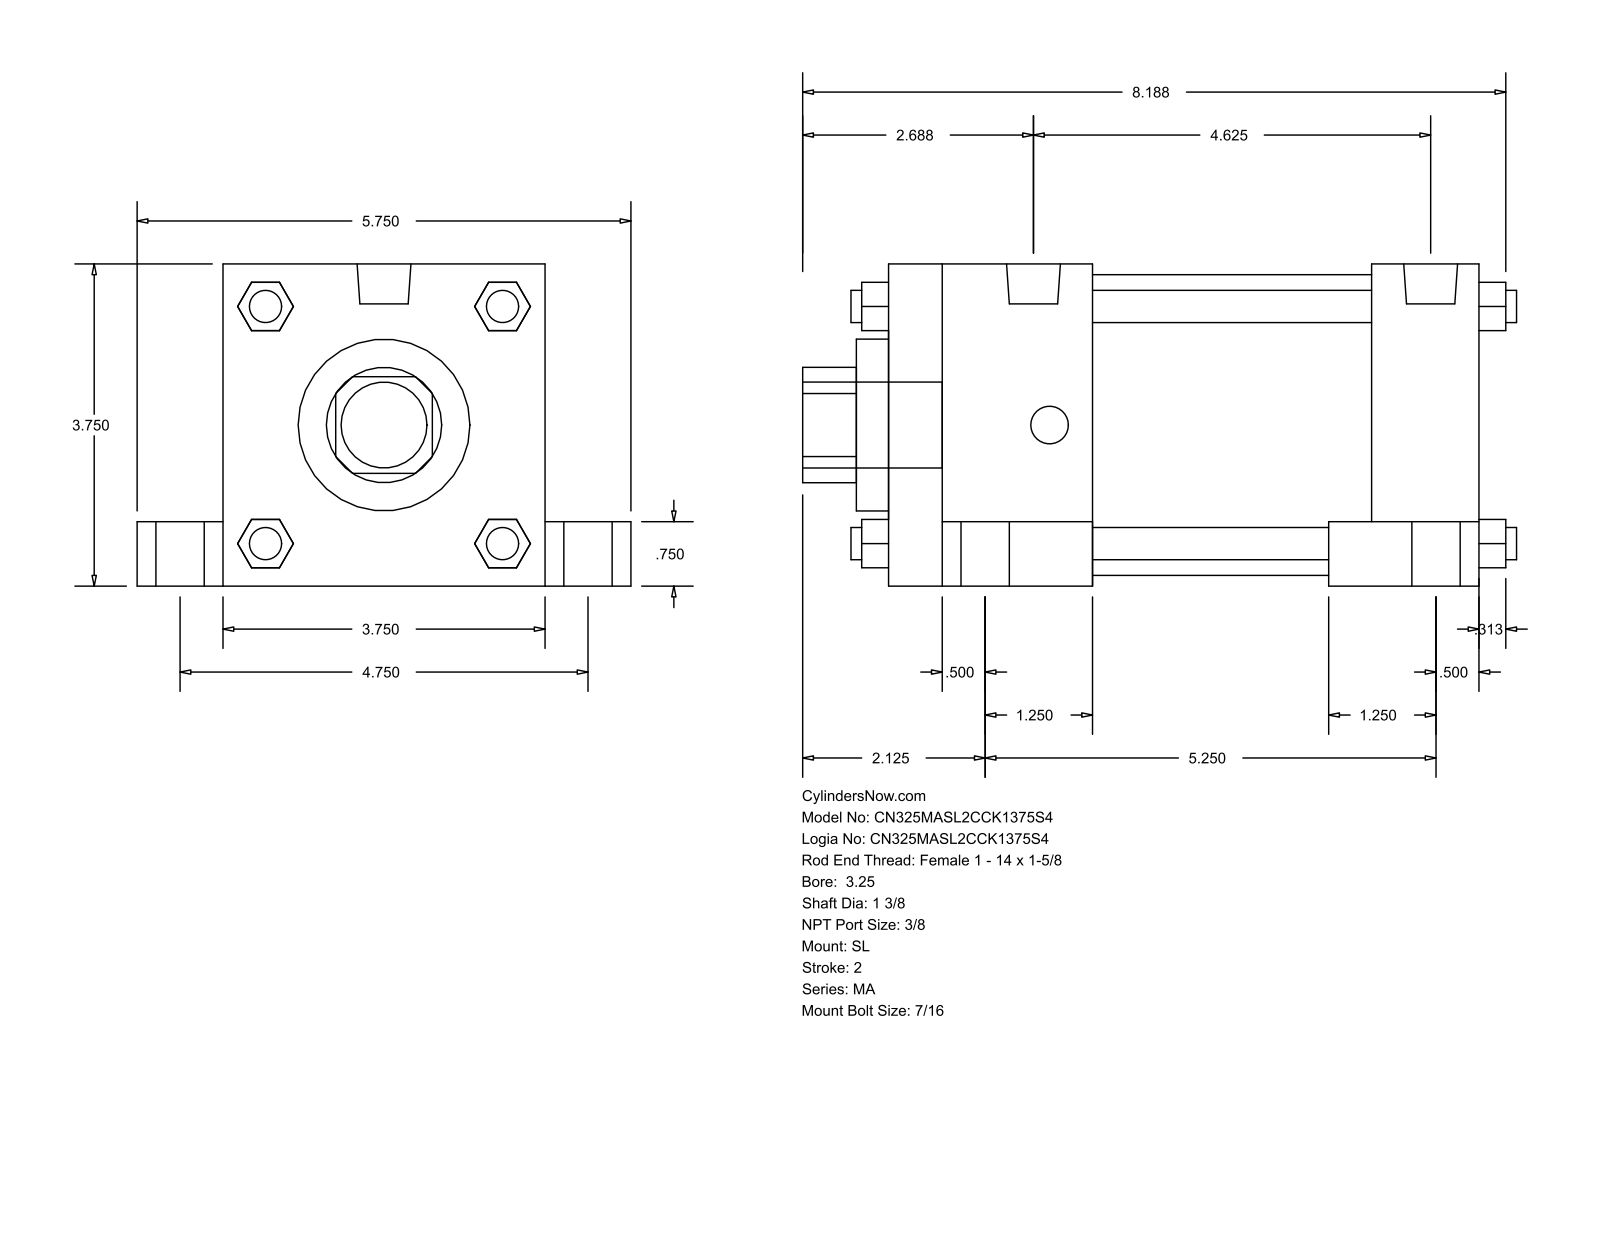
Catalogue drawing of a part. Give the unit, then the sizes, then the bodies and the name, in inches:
Units: inches
Overall size (bounding box): 8.313 × 5.75 × 3.75
Round holes (diameter × count): ⌀1.375 ×1, ⌀2 ×1, ⌀3.5 ×1
Round bosses / shafts (diameter × count): ⌀0.813 ×4, ⌀0.563 ×4, ⌀0.437 ×4, ⌀0.375 ×4, ⌀0.627 ×2, ⌀1 ×1
Partial cylindrical surfaces — rounded edges, fillets, slot ends (radius × count): R0.672 ×1
Main face-to-face distances: 3.75, 6.875, 1, 4.75, 5.625, 1.25, 2.375, 3.25, 4.5, 0.75
Bodies: 0 solids, 148 faces (112 planar, 36 cylindrical, 0 other)
Part name (STEP PRODUCT): MA_SL__0325_1.375
STEP written by: GSSL Pune (CONFIG_CONTROL_DESIGN)
